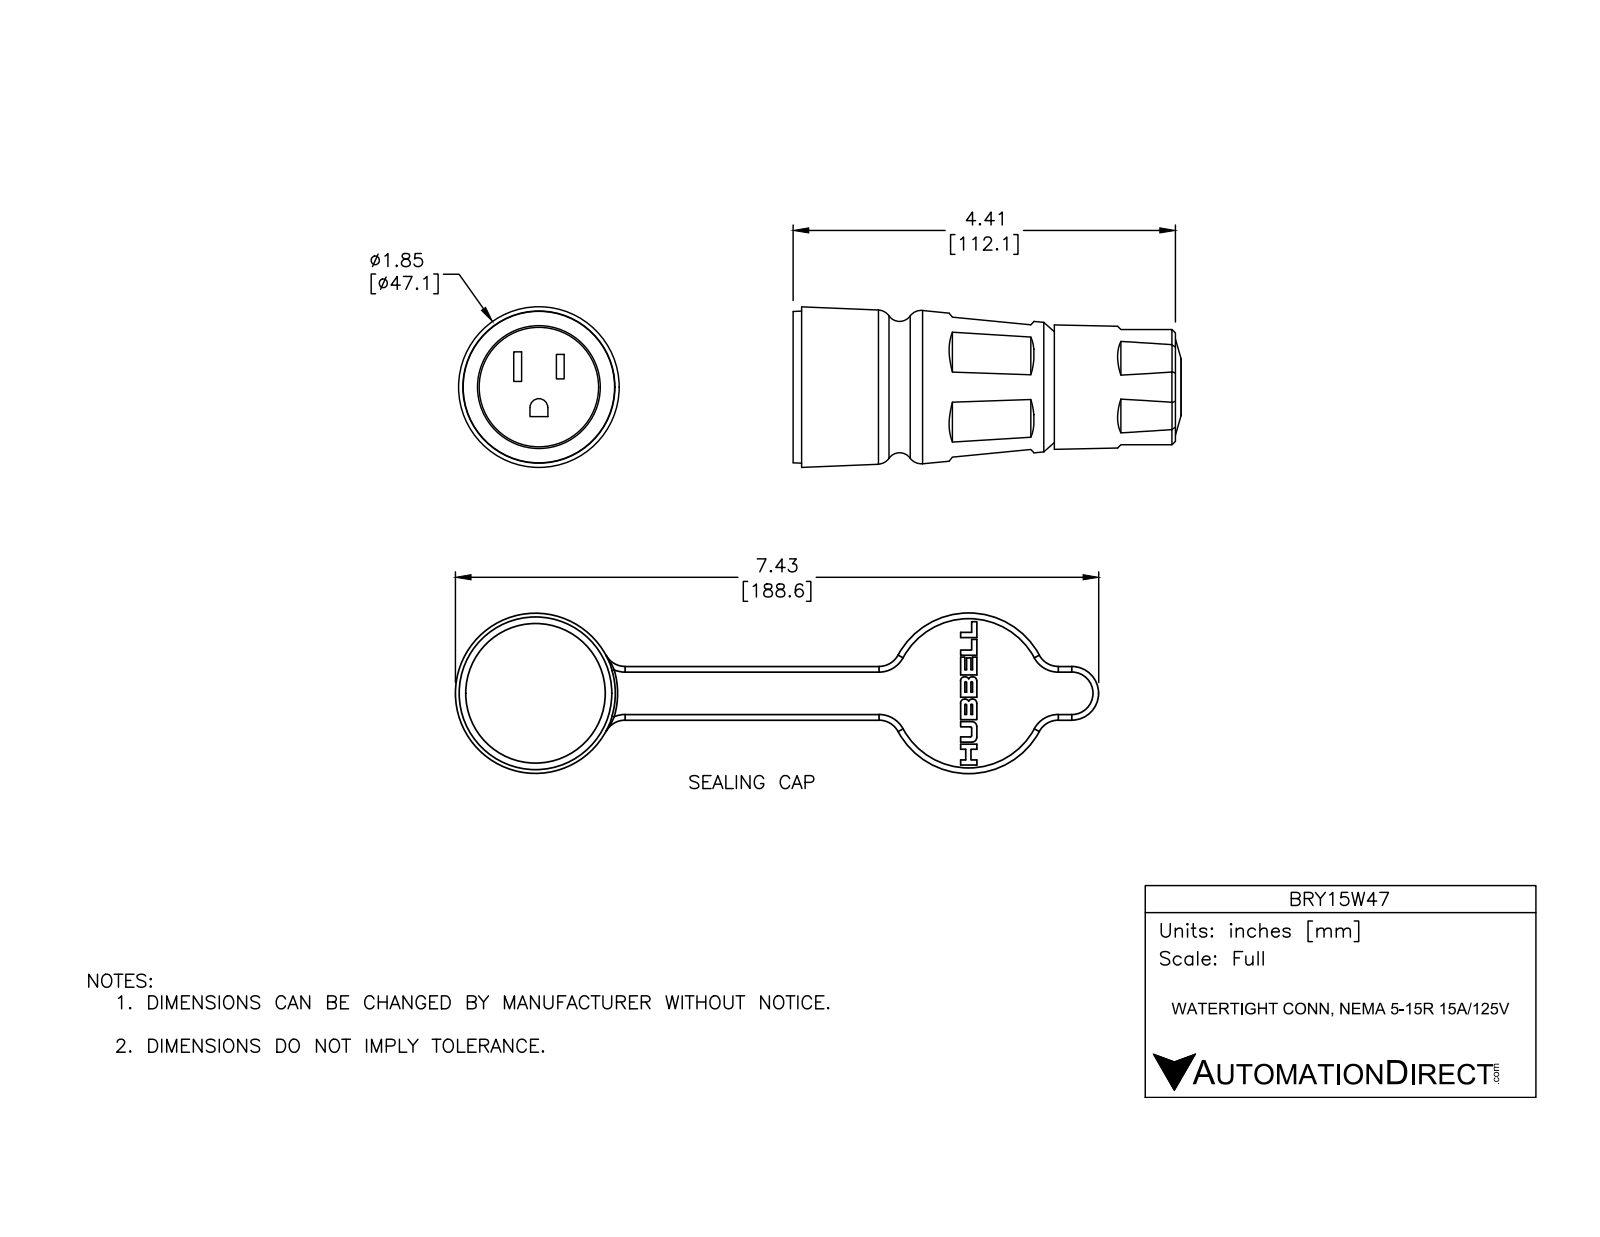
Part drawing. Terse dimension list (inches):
name: BRY15W-CAP; BRY15W47-CONNECTOR; BRY15W47
written by: SolidWorks 2016 (AUTOMOTIVE_DESIGN)
unit: in
bodies: 5 solids, 181 faces (79 planar, 46 cylindrical, 56 other)
size: 7.364 × 4.479 × 1.854
volume: 8.208 in³; area: 73.36 in²
holes: 1× ⌀0.561, 1× ⌀1.112, 1× ⌀1.22, 1× ⌀1.417, 1× ⌀1.535
bosses: 1× ⌀1.85, 1× ⌀1.772, 1× ⌀1.665, 1× ⌀1.472, 1× ⌀1.378, 1× ⌀0.993
rounds: 4× R0.059, 4× R0.236, 2× R0.157, 1× R0.103, 1× R0.315
face distances: 0.128, 0.202, 0.33, 0.866, 0.665, 0.537, 0.422, 0.22, 0.093, 0.444
hole spacings: 4.941
